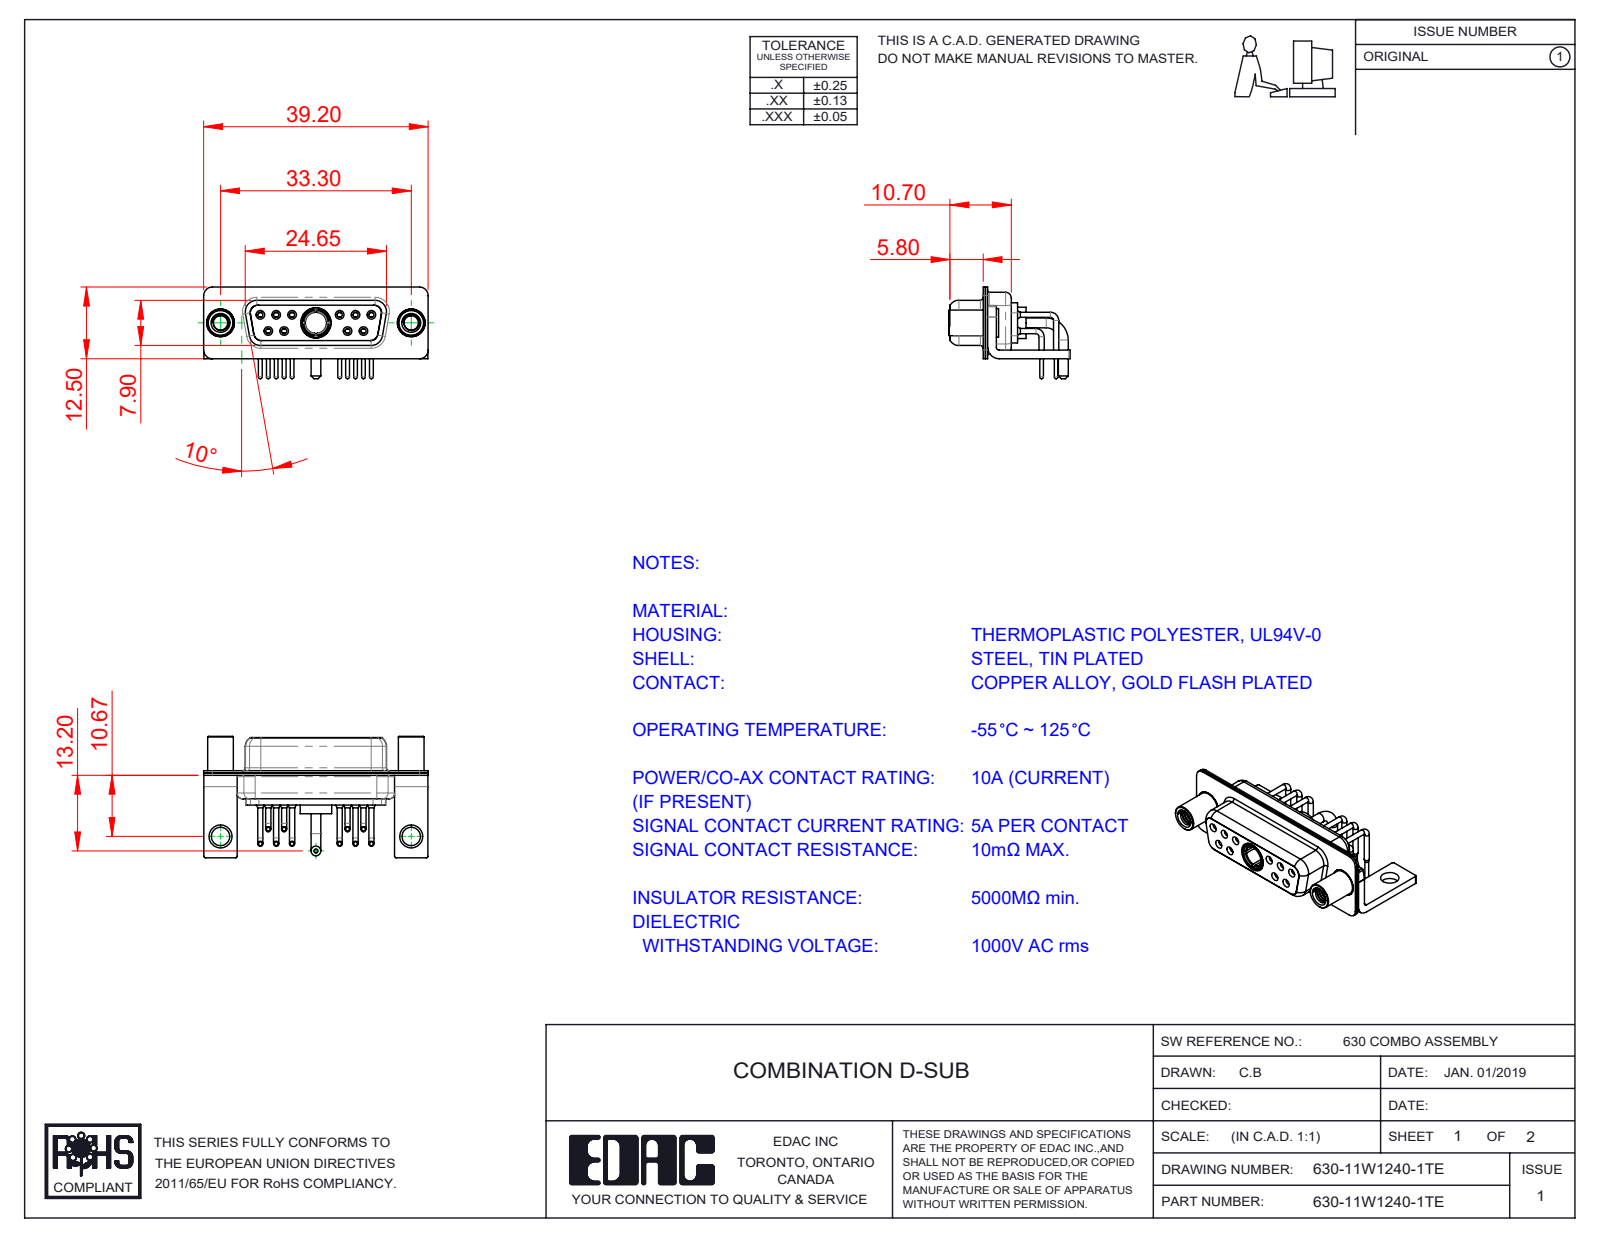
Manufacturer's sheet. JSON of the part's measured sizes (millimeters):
{"part_name": "Power Socket_10A RA; 630Combo Stabilizer Bracket; 630Combo Housing_11W1; 630Combo Shell Rear_15 Contacts (+5 more)", "step_written_by": "SolidWorks 2020 (CONFIG_CONTROL_DESIGN)", "units": "millimeters", "bodies": {"solids": 19, "faces": 985, "planar": 268, "cylindrical": 464, "other": 253}, "overall_size": [39.2, 21.2, 16], "volume_mm3": 2972, "surface_area_mm2": 7146, "round_holes": [[0.9, 10], [1.1, 10], [1.5, 10], [2, 10], [1.7, 6], [1.6, 4], [4.85, 3], [2.5, 2], [3.2, 2], [4, 2], [4.05, 2], [3.7, 1]], "round_bosses_or_shafts": [[0.9, 10], [0.65, 10], [1.6, 6], [5, 2], [4.95, 2], [4.8, 2], [4.5, 2], [1.7, 2]], "partial_cylinders_radius": [[0.25, 16], [1.5, 16], [2, 13], [1.35, 12], [1.6, 8], [0.5, 5], [0.6, 4], [0.65, 4]], "face_to_face_distances": [0.4, 0.8, 1.4, 0.45, 8.45, 1.5, 1.8, 8.9, 6.2, 2.3], "hole_center_spacings": [3.16, 2.77, 13.85, 11.08, 16.62, 5.03, 5.04, 5.54]}
